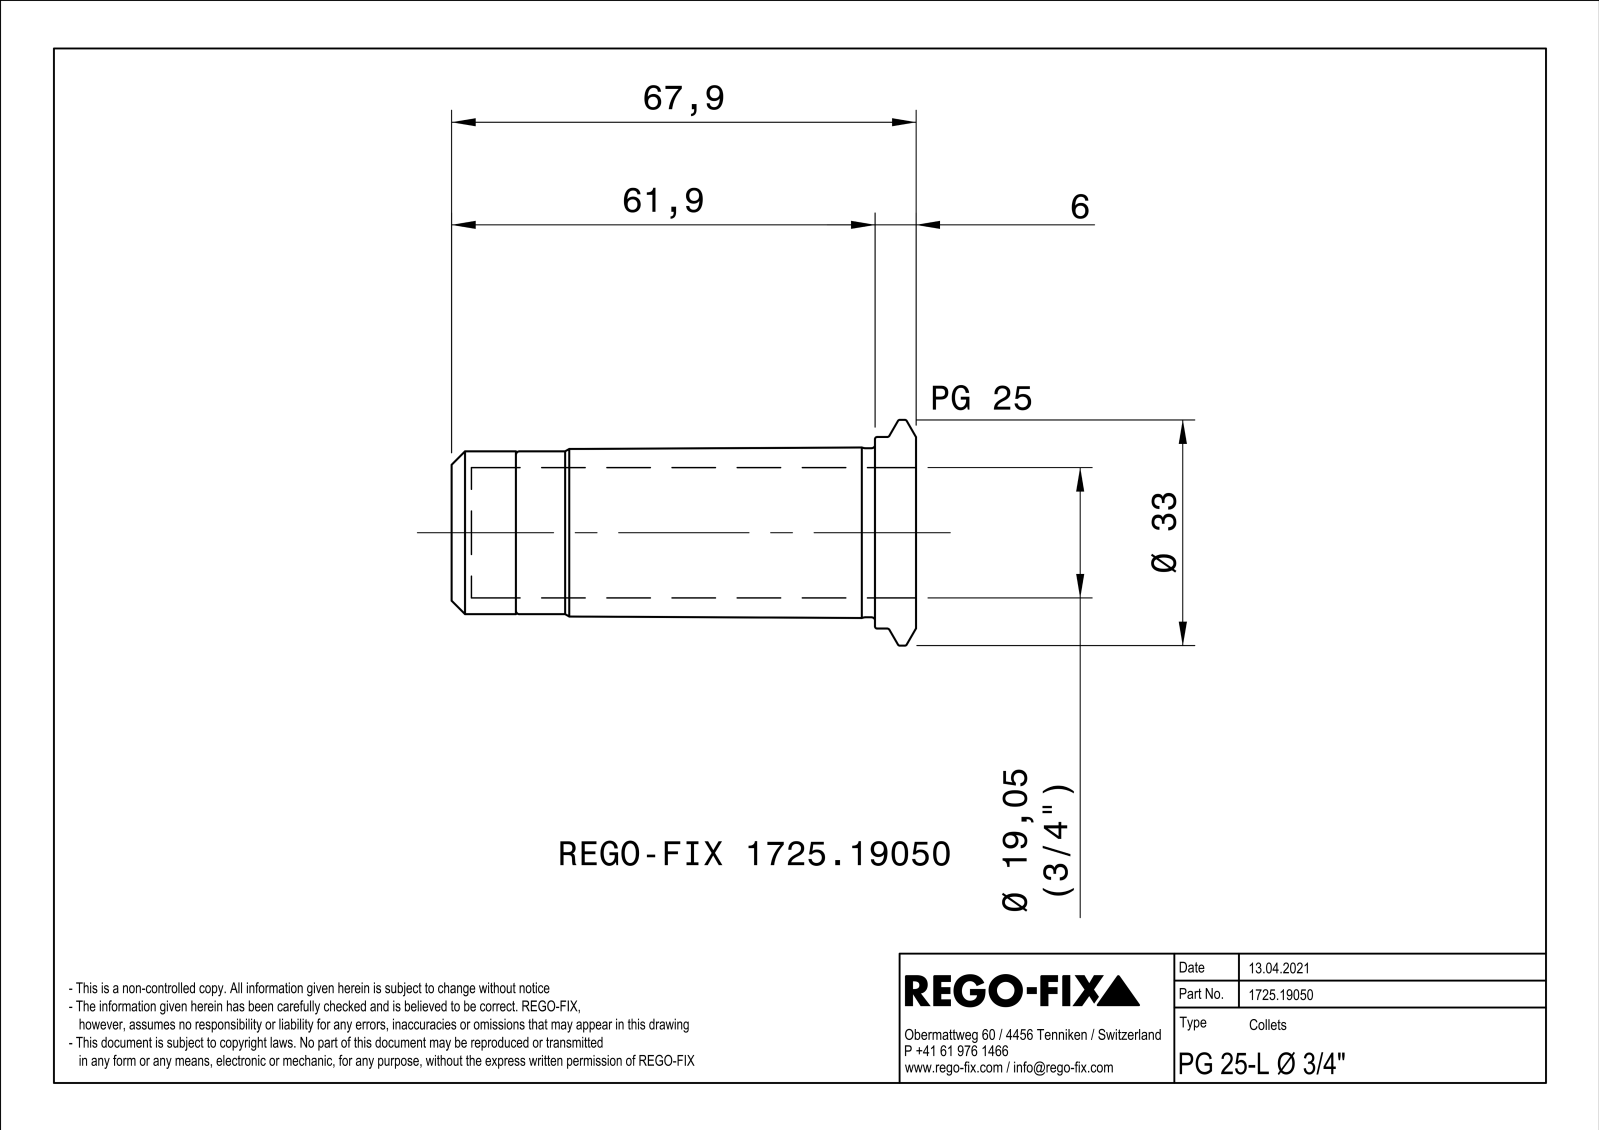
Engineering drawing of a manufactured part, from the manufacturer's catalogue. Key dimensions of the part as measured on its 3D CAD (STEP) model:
Part name (STEP PRODUCT): NOCUT
STEP written by: SIEMENS PLM Software Solid Edge ST10 (AUTOMOTIVE_DESIGN)
Units: millimetres
Bodies: 0 solids, 62 faces (18 planar, 13 cylindrical, 31 other)
Overall size (bounding box): 58.5 × 33 × 32.99
Round holes (diameter × count): ⌀19.05 ×1, ⌀22 ×1, ⌀22.2 ×1
Round bosses / shafts (diameter × count): ⌀33 ×1, ⌀28 ×1, ⌀24.7 ×1, ⌀23.8 ×1
Main face-to-face distances: 1, 6, 52.5, 58.5, 46.5
